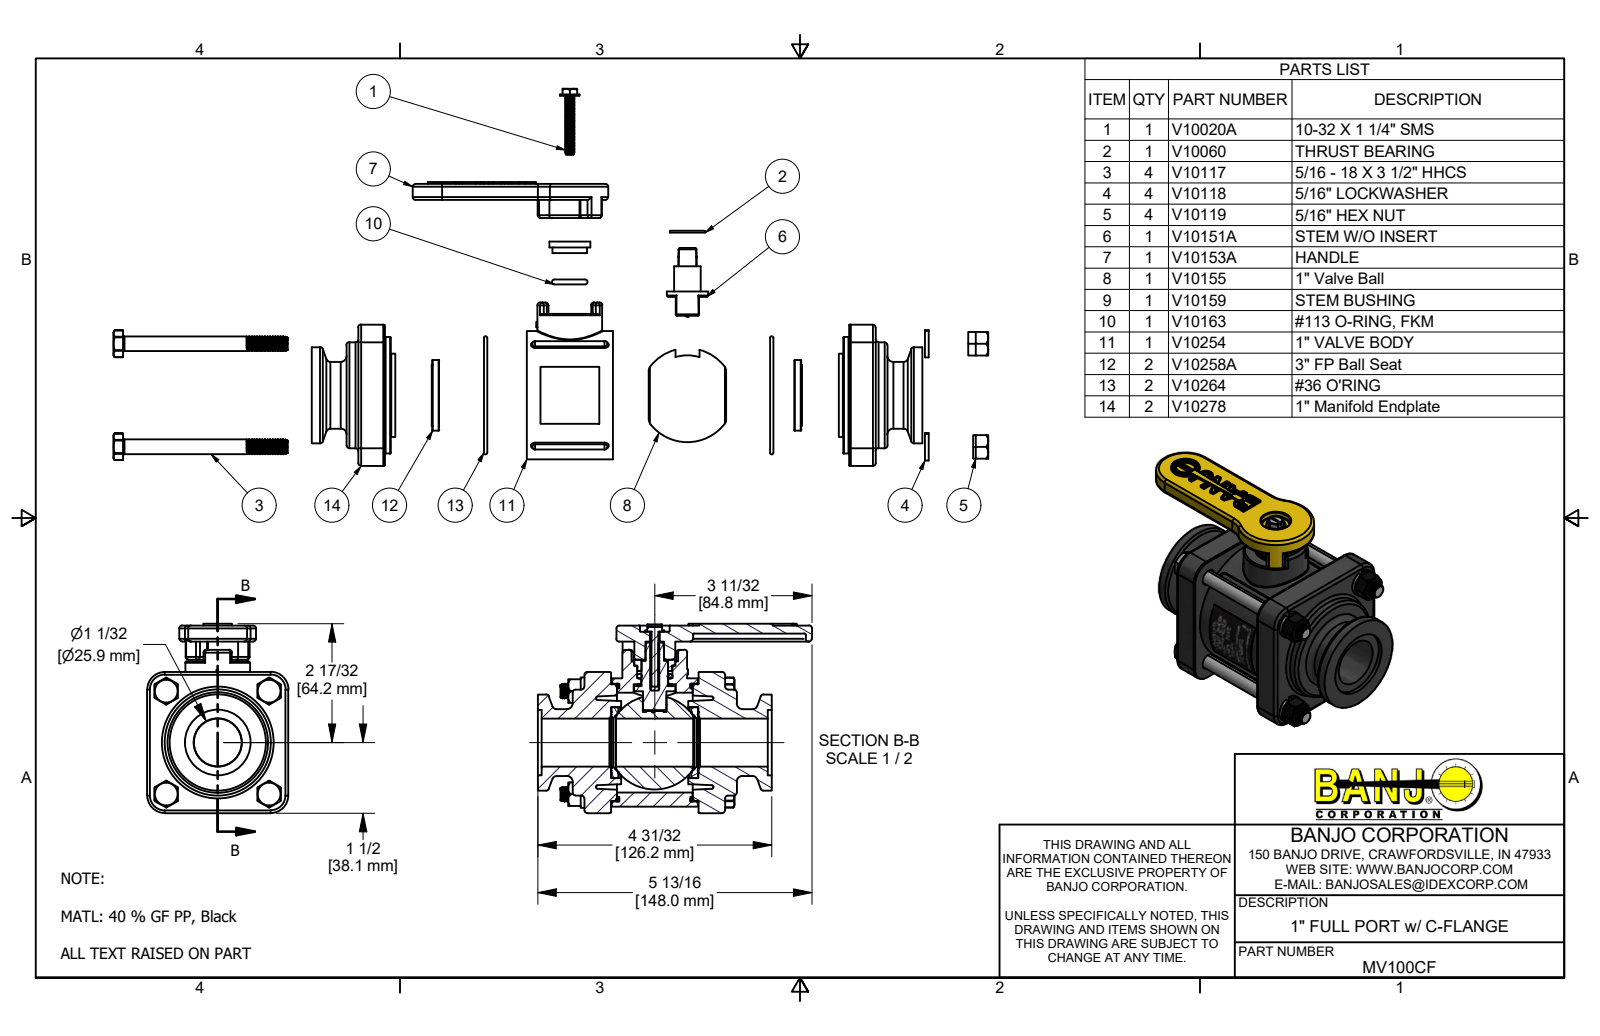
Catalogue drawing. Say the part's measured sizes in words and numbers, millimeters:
The part is named "MV100CF; V10254; VL1001-D2.725; V10060 (+8 more)". Its 3-D file was written by "Autodesk Inventor 2019 (AUTOMOTIVE_DESIGN)". It is 27 solids with 1857 faces: 487 planar, 659 cylindrical and 711 other. Overall it measures 148 by 102.3 by 76.2 millimeters. Its volume is 381 000 cubic millimeters and its surface area 133 300 square millimeters. Round holes: 4 of diameter 6.4, 4 of diameter 8.2, 4 of diameter 8.9, 1 of diameter 3.6, 1 of diameter 5.1, 1 of diameter 10.4, 1 of diameter 14.2, 1 of diameter 14.3, 1 of diameter 14.5, 1 of diameter 14.7, 1 of diameter 16, 1 of diameter 19.1. Round bosses or shafts: 60 of diameter 6.8, 39 of diameter 4.2, 4 of diameter 14.8, 4 of diameter 8, 1 of diameter 62.9, 1 of diameter 58.5, 1 of diameter 57.2, 1 of diameter 51.8. Partial cylindrical surfaces (rounded edges, fillets, slot ends): 46 of radius 1.5, 32 of radius 0.8, 10 of radius 3.4, 8 of radius 1.6, 8 of radius 9.5, 4 of radius 0.4, 4 of radius 2, 4 of radius 7.2. The main face-to-face distances are 14.4, 61.6, 3.2, 17.5, 58.4, 44.1, 76.2, 75.9, 25.1, 39.5. The hole center spacings are 39.3, 55.6, 78.6, 69.
